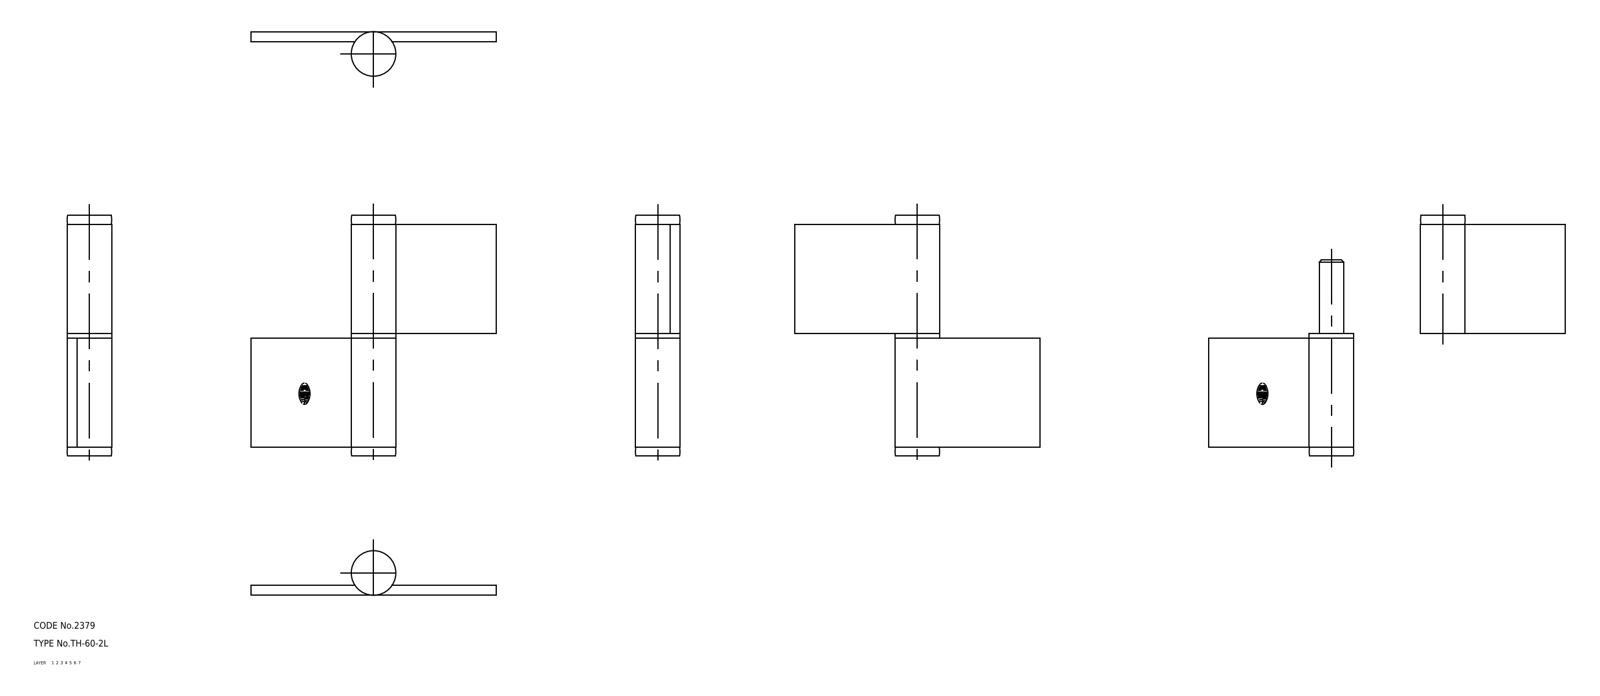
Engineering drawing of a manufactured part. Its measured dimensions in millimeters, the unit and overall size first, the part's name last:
Units: millimetres
Overall size (bounding box): 110 × 108 × 20
Volume: 54 192 mm³ · Surface area: 27 012 mm²
Bodies: 5 solids, 34 faces (0 planar, 0 cylindrical, 34 other)
Part name (STEP PRODUCT): hinge piece; washer; shaft; rivet (+1 more)
STEP written by: CADfix (AUTOMOTIVE_DESIGN)
